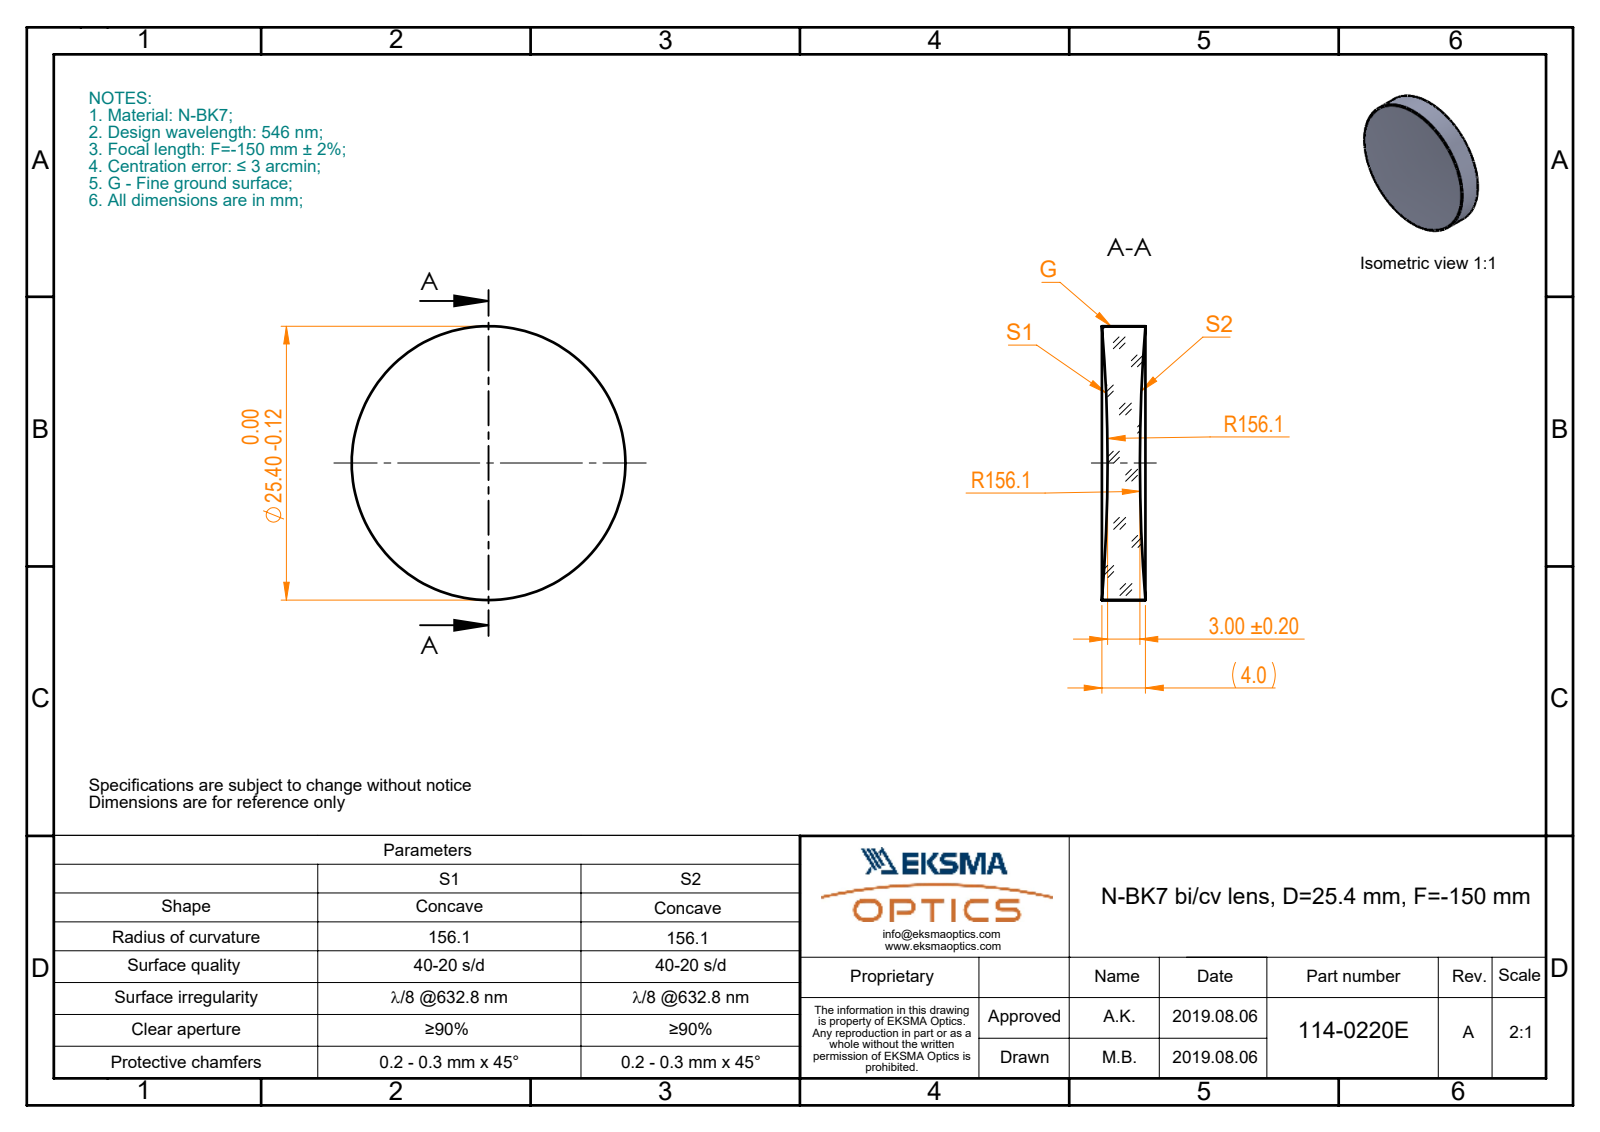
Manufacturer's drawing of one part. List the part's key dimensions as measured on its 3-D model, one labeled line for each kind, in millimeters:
Part name (STEP PRODUCT): 114-0220E BK7 bi-cv 25.4 F-150
STEP written by: SolidWorks 2017 (CONFIG_CONTROL_DESIGN)
Units: millimetres
Bodies: 1 solid, 6 faces (0 planar, 2 cylindrical, 4 other)
Overall size (bounding box): 25.4 × 25.4 × 4.04
Volume: 1 782 mm³ · Surface area: 1 337 mm²
Round bosses / shafts (diameter × count): ⌀25.4 ×1
